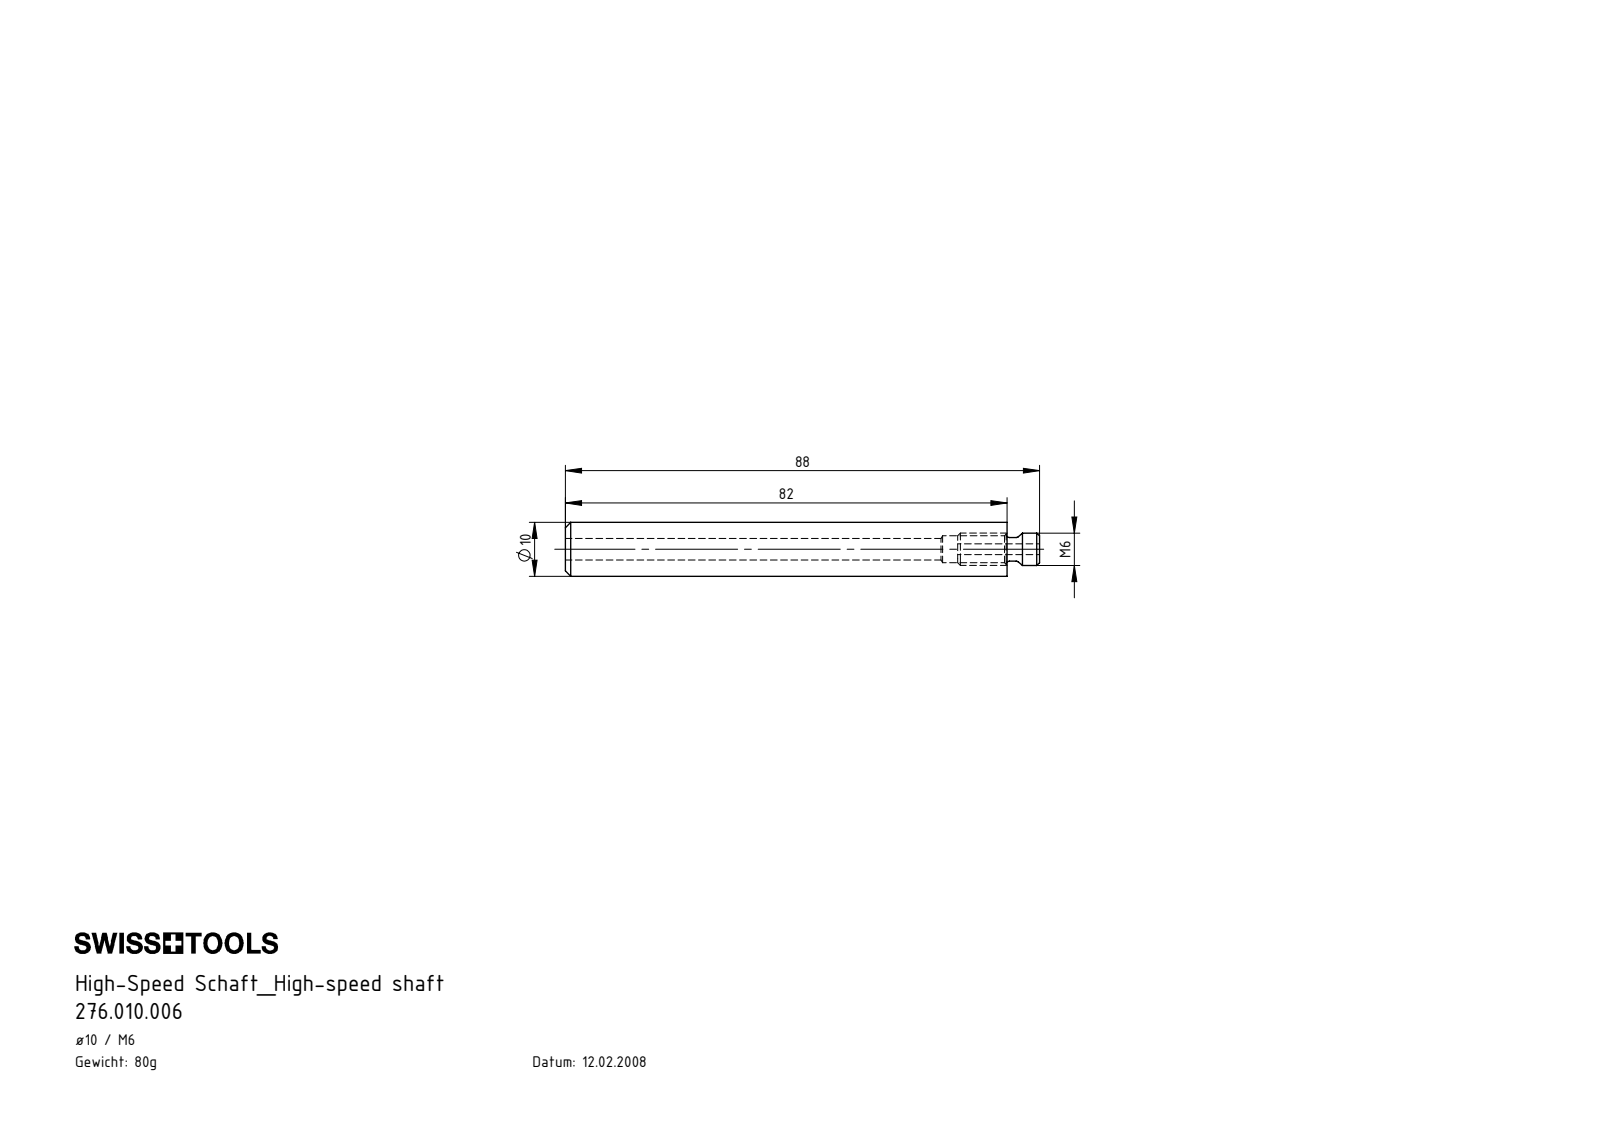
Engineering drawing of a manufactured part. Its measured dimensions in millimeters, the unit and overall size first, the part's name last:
Units: millimetres
Overall size (bounding box): 88 × 10 × 10
Round holes (diameter × count): ⌀2 ×1, ⌀4 ×1, ⌀5 ×1
Round bosses / shafts (diameter × count): ⌀10 ×1, ⌀6 ×1, ⌀4.4 ×1
Main face-to-face distances: 82, 88, 6, 72.8, 9.2, 15.2, 81.8, 9, 6.2
Volume: 5 652 mm³ · Surface area: 4 171 mm²
Bodies: 2 solids, 35 faces (5 planar, 14 cylindrical, 16 other)
Part name (STEP PRODUCT): HM1-U10.001.082_A; HM1-BG1.006.015_A; U10-HS6.K01.082_A
STEP written by: SolidWorks 2015 (AUTOMOTIVE_DESIGN)
